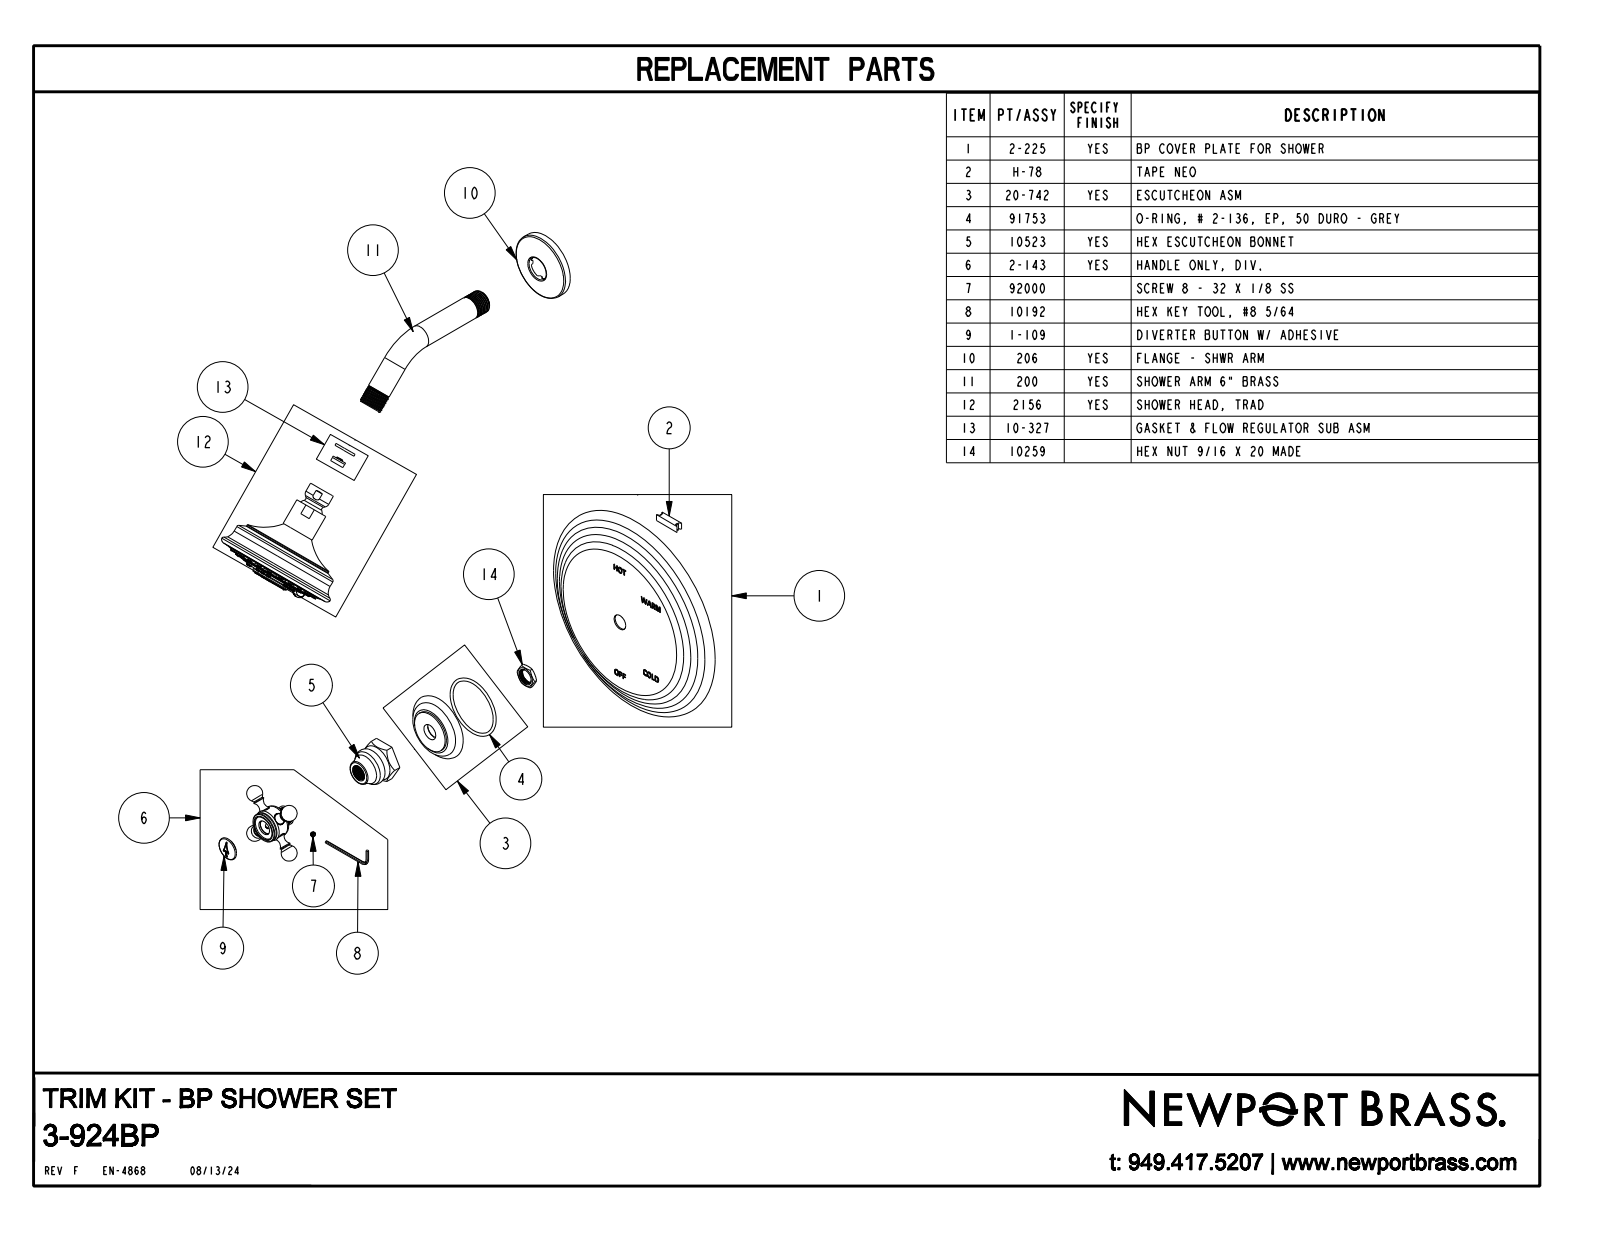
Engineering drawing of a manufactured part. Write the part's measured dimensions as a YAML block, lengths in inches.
part_name: "3-924BP"
step_written_by: "CREO PARAMETRIC BY PTC INC, 2018400 (CONFIG_CONTROL_DESIGN)"
units: inches
bodies: {solids: 2, faces: 1429, planar: 295, cylindrical: 225, other: 909}
overall_size: [17.065, 8.25, 7.75]
volume: 51.7
surface_area: 193
round_holes:
  - {diameter: 0.059, count: 8}
  - {diameter: 0.41, count: 2}
  - {diameter: 0.855, count: 1}
  - {diameter: 0.925, count: 1}
round_bosses_or_shafts:
  - {diameter: 0.142, count: 39}
  - {diameter: 0.165, count: 23}
  - {diameter: 0.813, count: 2}
  - {diameter: 0.392, count: 2}
  - {diameter: 3.81, count: 1}
  - {diameter: 3.724, count: 1}
  - {diameter: 3.24, count: 1}
  - {diameter: 2.38, count: 1}
partial_cylinders:
  - {radius: 0.079, count: 8}
  - {radius: 0.015, count: 2}
  - {radius: 0.02, count: 2}
  - {radius: 1, count: 2}
  - {radius: 1.02, count: 2}
  - {radius: 0.02, count: 1}
  - {radius: 0.138, count: 1}
  - {radius: 0.472, count: 1}
face_to_face_distances: [0.754, 0.063, 0.118, 0.181, 1.313, 0.062, 2.441, 1.687, 1.129, 0.375]
hole_center_spacings: [0.443, 0.579, 0.818, 0.819, 1.069, 0.443, 0.578, 1.069]
